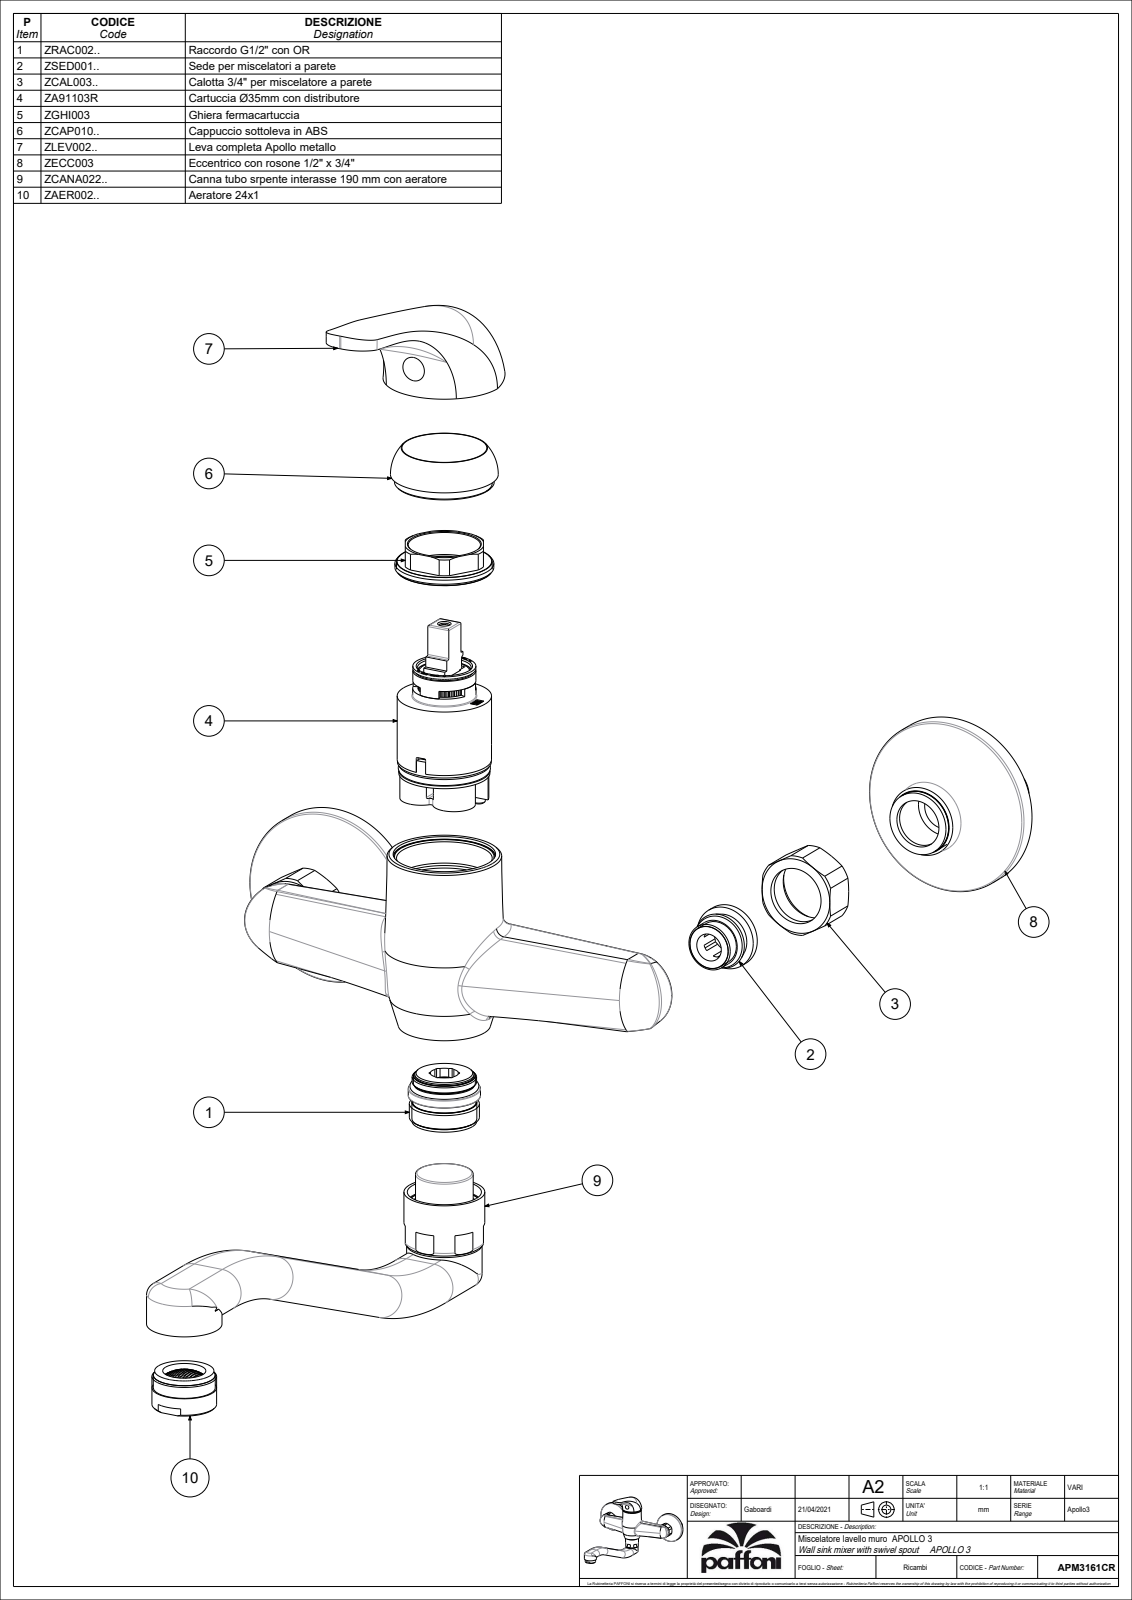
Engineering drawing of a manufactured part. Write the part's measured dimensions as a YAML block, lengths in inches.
part_name: "APM3161CR"
step_written_by: "CREO PARAMETRIC BY PTC INC, 2020044 (CONFIG_CONTROL_DESIGN)"
units: inches
bodies: {solids: 5, faces: 3010, planar: 2151, cylindrical: 411, other: 448}
overall_size: [10.079, 8.504, 5.917]
volume: 9.66
surface_area: 226.2
round_holes:
  - {diameter: 0.354, count: 3}
  - {diameter: 0.472, count: 3}
  - {diameter: 0.157, count: 2}
  - {diameter: 0.276, count: 2}
  - {diameter: 0.315, count: 2}
  - {diameter: 0.413, count: 2}
  - {diameter: 0.63, count: 2}
  - {diameter: 0.709, count: 2}
  - {diameter: 0.846, count: 2}
  - {diameter: 0.949, count: 2}
  - {diameter: 0.984, count: 2}
  - {diameter: 1.051, count: 2}
round_bosses_or_shafts:
  - {diameter: 0.945, count: 3}
  - {diameter: 2.598, count: 2}
  - {diameter: 1.102, count: 2}
  - {diameter: 1.008, count: 2}
  - {diameter: 1.378, count: 1}
  - {diameter: 1.37, count: 1}
  - {diameter: 1.331, count: 1}
  - {diameter: 1.268, count: 1}
partial_cylinders:
  - {radius: 0.02, count: 41}
  - {radius: 0.039, count: 12}
  - {radius: 0.006, count: 11}
  - {radius: 0.012, count: 9}
  - {radius: 0.283, count: 6}
  - {radius: 0.315, count: 6}
  - {radius: 0.276, count: 4}
  - {radius: 0.138, count: 2}
face_to_face_distances: [0.031, 0.138, 0.02, 0.598, 0.118, 0.354, 0.63, 0.335, 0.236, 0.472]
hole_center_spacings: [0.028, 0.335, 0.339, 0.513, 0.52, 0.532, 3.52, 3.733]
